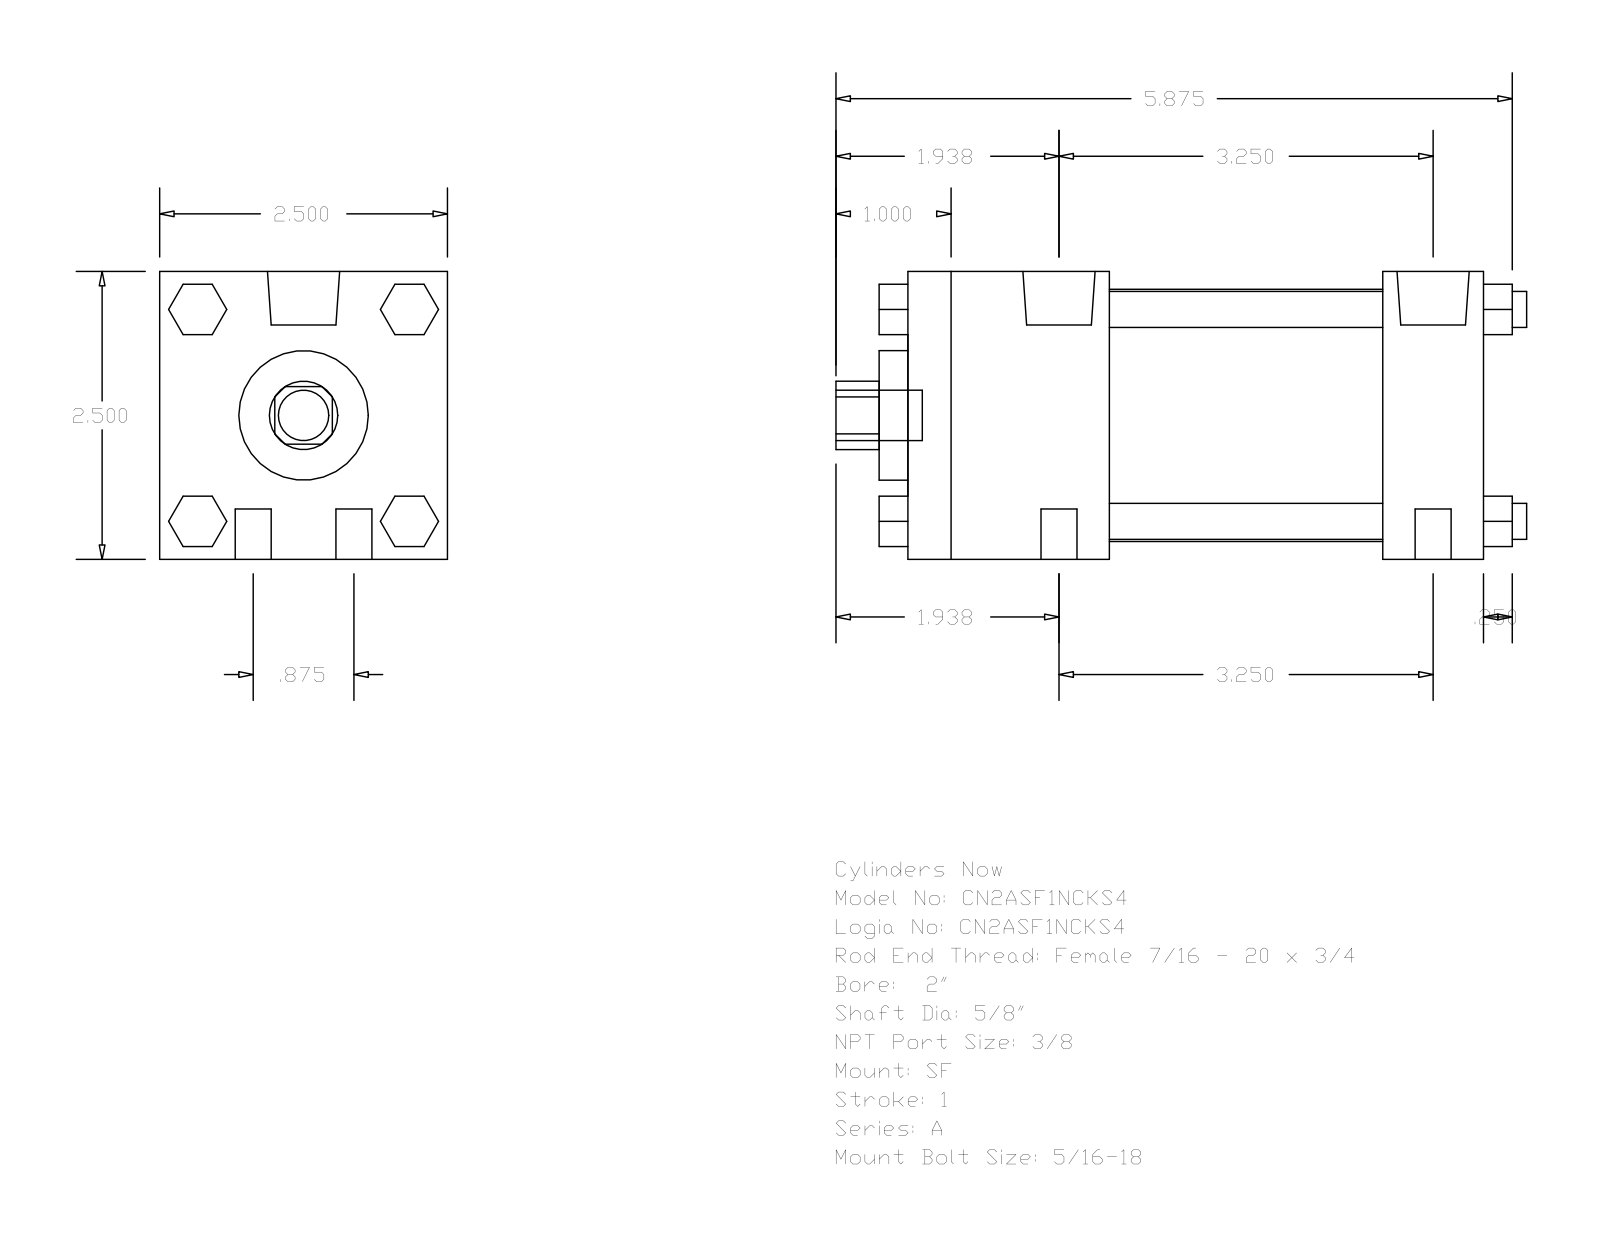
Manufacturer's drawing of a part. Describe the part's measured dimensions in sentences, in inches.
The part is named "A_SF__0200_0.625". Its 3-D file was written by "GSSL Pune (CONFIG_CONTROL_DESIGN)". It is 0 solids with 124 faces: 94 planar, 30 cylindrical and 0 other. Overall it measures 6 by 2.5 by 2.5 inches. Round holes: 1 of diameter 0.625, 1 of diameter 1.125, 1 of diameter 2.19. Round bosses or shafts: 8 of diameter 0.313, 2 of diameter 0.627, 2 of diameter 0.219, 1 of diameter 0.437. Partial cylindrical surfaces (rounded edges, fillets, slot ends): 1 of radius 0.297. The main face-to-face distances are 2.5, 5, 4.125, 0.875, 1.75, 2.375, 3.25, 2, 5.25, 0.25.
